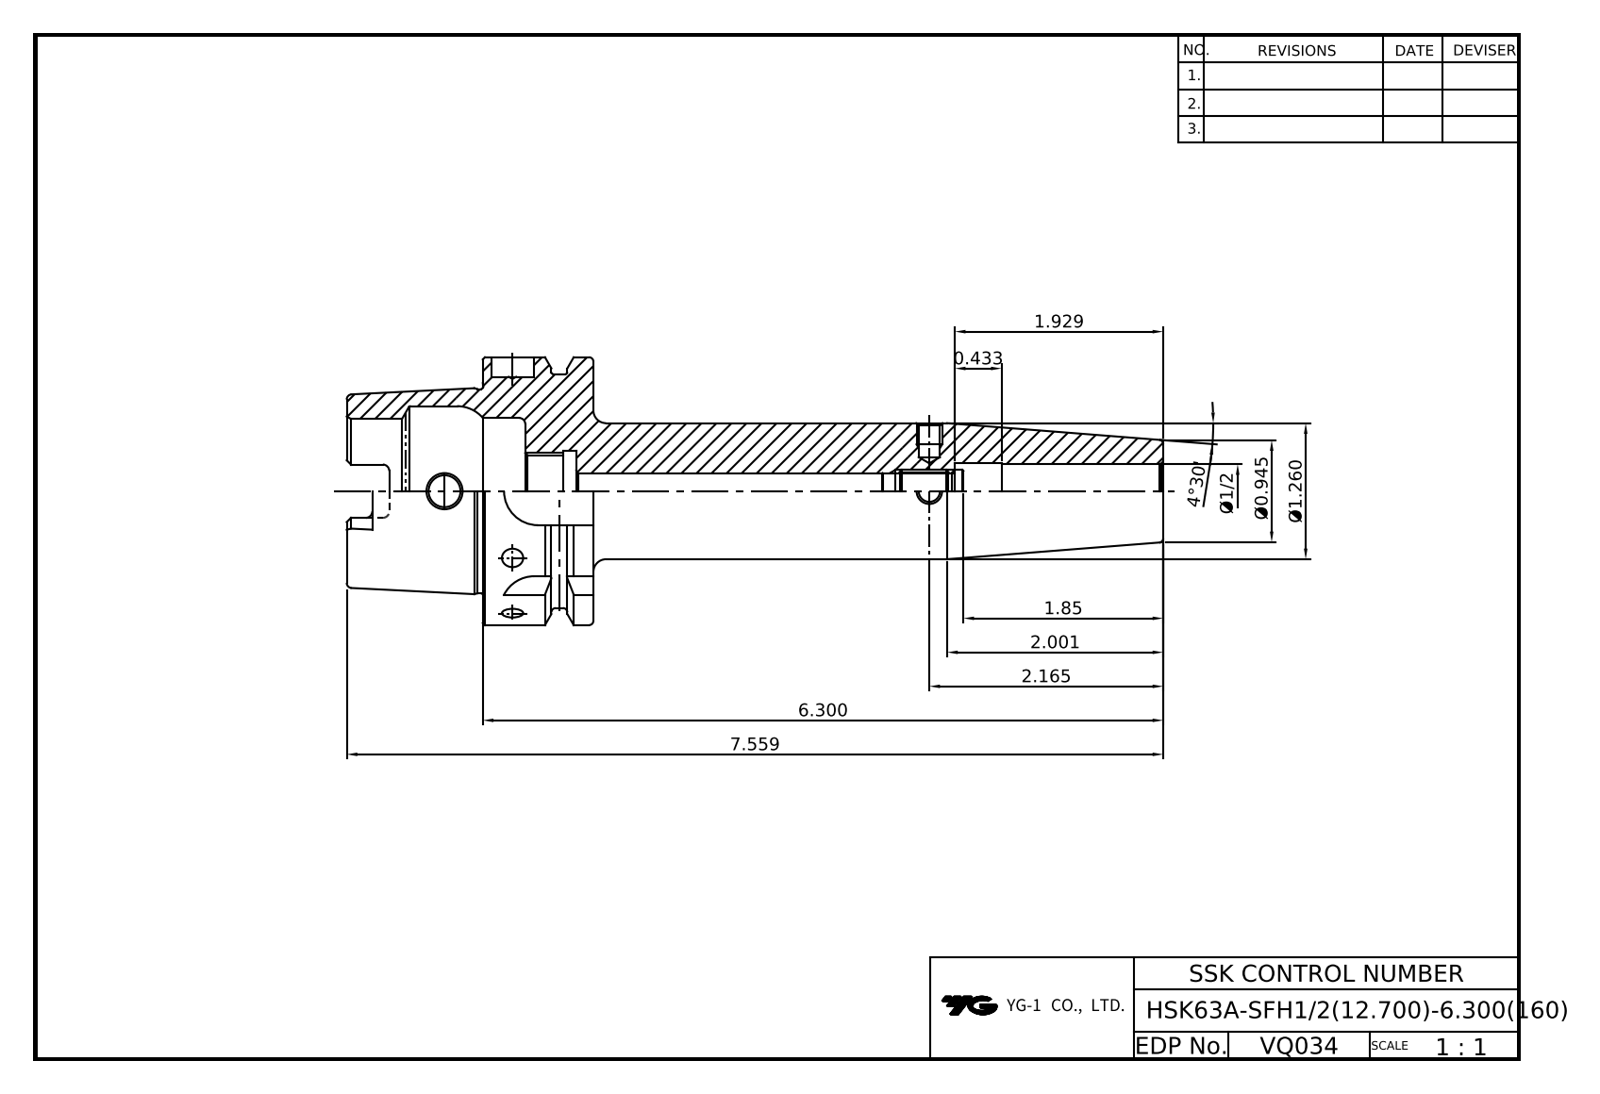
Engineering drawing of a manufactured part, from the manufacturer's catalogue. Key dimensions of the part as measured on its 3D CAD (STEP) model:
Part name (STEP PRODUCT): LO-HSK63A-SFH12.7-160
STEP written by: Autodesk Inventor 2022 (AUTOMOTIVE_DESIGN)
Units: millimetres
Bodies: 1 solid, 118 faces (43 planar, 35 cylindrical, 40 other)
Overall size (bounding box): 192 × 63 × 63
Volume: 169 023 mm³ · Surface area: 38 867 mm²
Round holes (diameter × count): ⌀7.5 ×1, ⌀8 ×1, ⌀8.4 ×1, ⌀8.92 ×1, ⌀10 ×1, ⌀12.7 ×1, ⌀13.9 ×1, ⌀16.92 ×1, ⌀19 ×1, ⌀34 ×1, ⌀40 ×1
Round bosses / shafts (diameter × count): ⌀63 ×1, ⌀55 ×1, ⌀48.04 ×1, ⌀32 ×1
Partial cylindrical surfaces — rounded edges, fillets, slot ends (radius × count): R1.5 ×6, R2.88 ×4, R8 ×4
Main face-to-face distances: 26, 10, 16, 32, 42, 58, 53, 22, 4, 12
